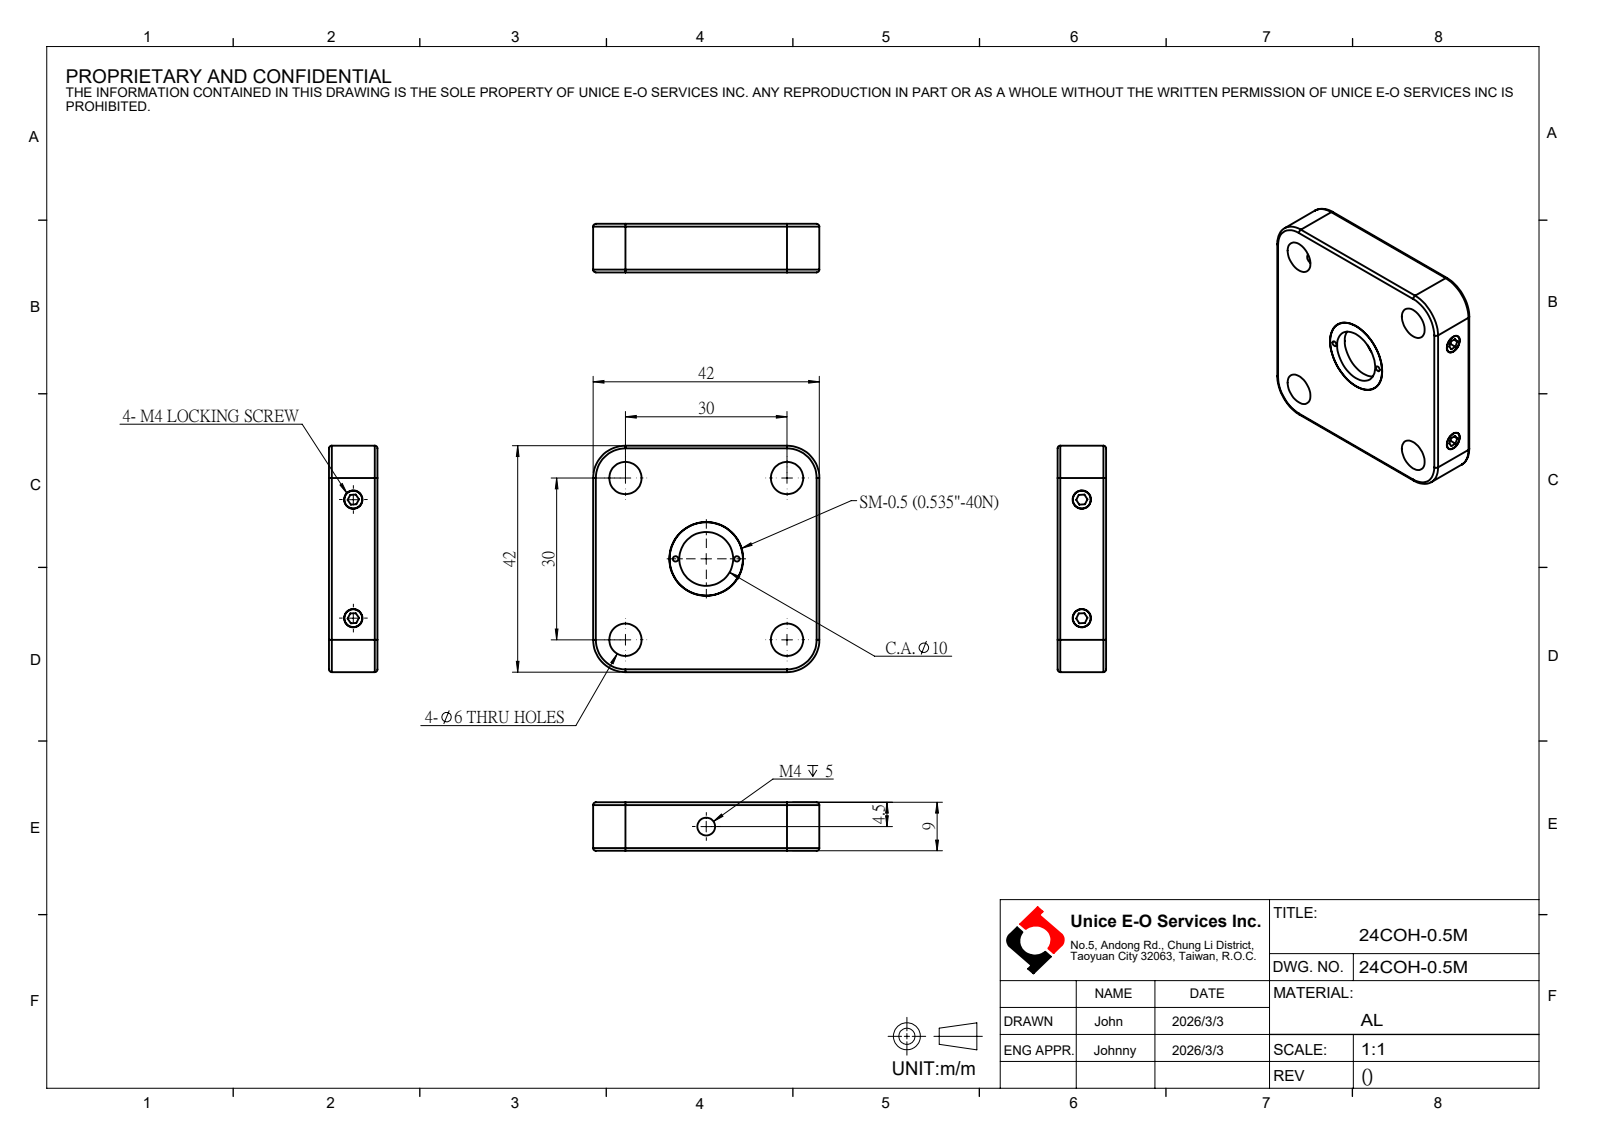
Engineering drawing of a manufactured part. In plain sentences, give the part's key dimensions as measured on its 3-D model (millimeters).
The part is named "24COH-0.5M". Its 3-D file was written by "SolidWorks 2024 (CONFIG_CONTROL_DESIGN)". It is 0 solids with 94 faces: 42 planar, 40 cylindrical and 12 other. Overall it measures 42 by 42 by 9 millimeters. Round holes: 4 of diameter 6, 2 of diameter 1, 1 of diameter 3.3, 1 of diameter 10, 1 of diameter 12.7. Round bosses or shafts: 1 of diameter 13.6. Partial cylindrical surfaces (rounded edges, fillets, slot ends): 8 of radius 0.5, 4 of radius 6. The main face-to-face distances are 9, 42, 2, 7, 5, 4, 38, 1.82, 34, 21.96. The hole center spacings are 17.65, 21.21, 25.56, 30, 5.7, 42.43, 11.4.
